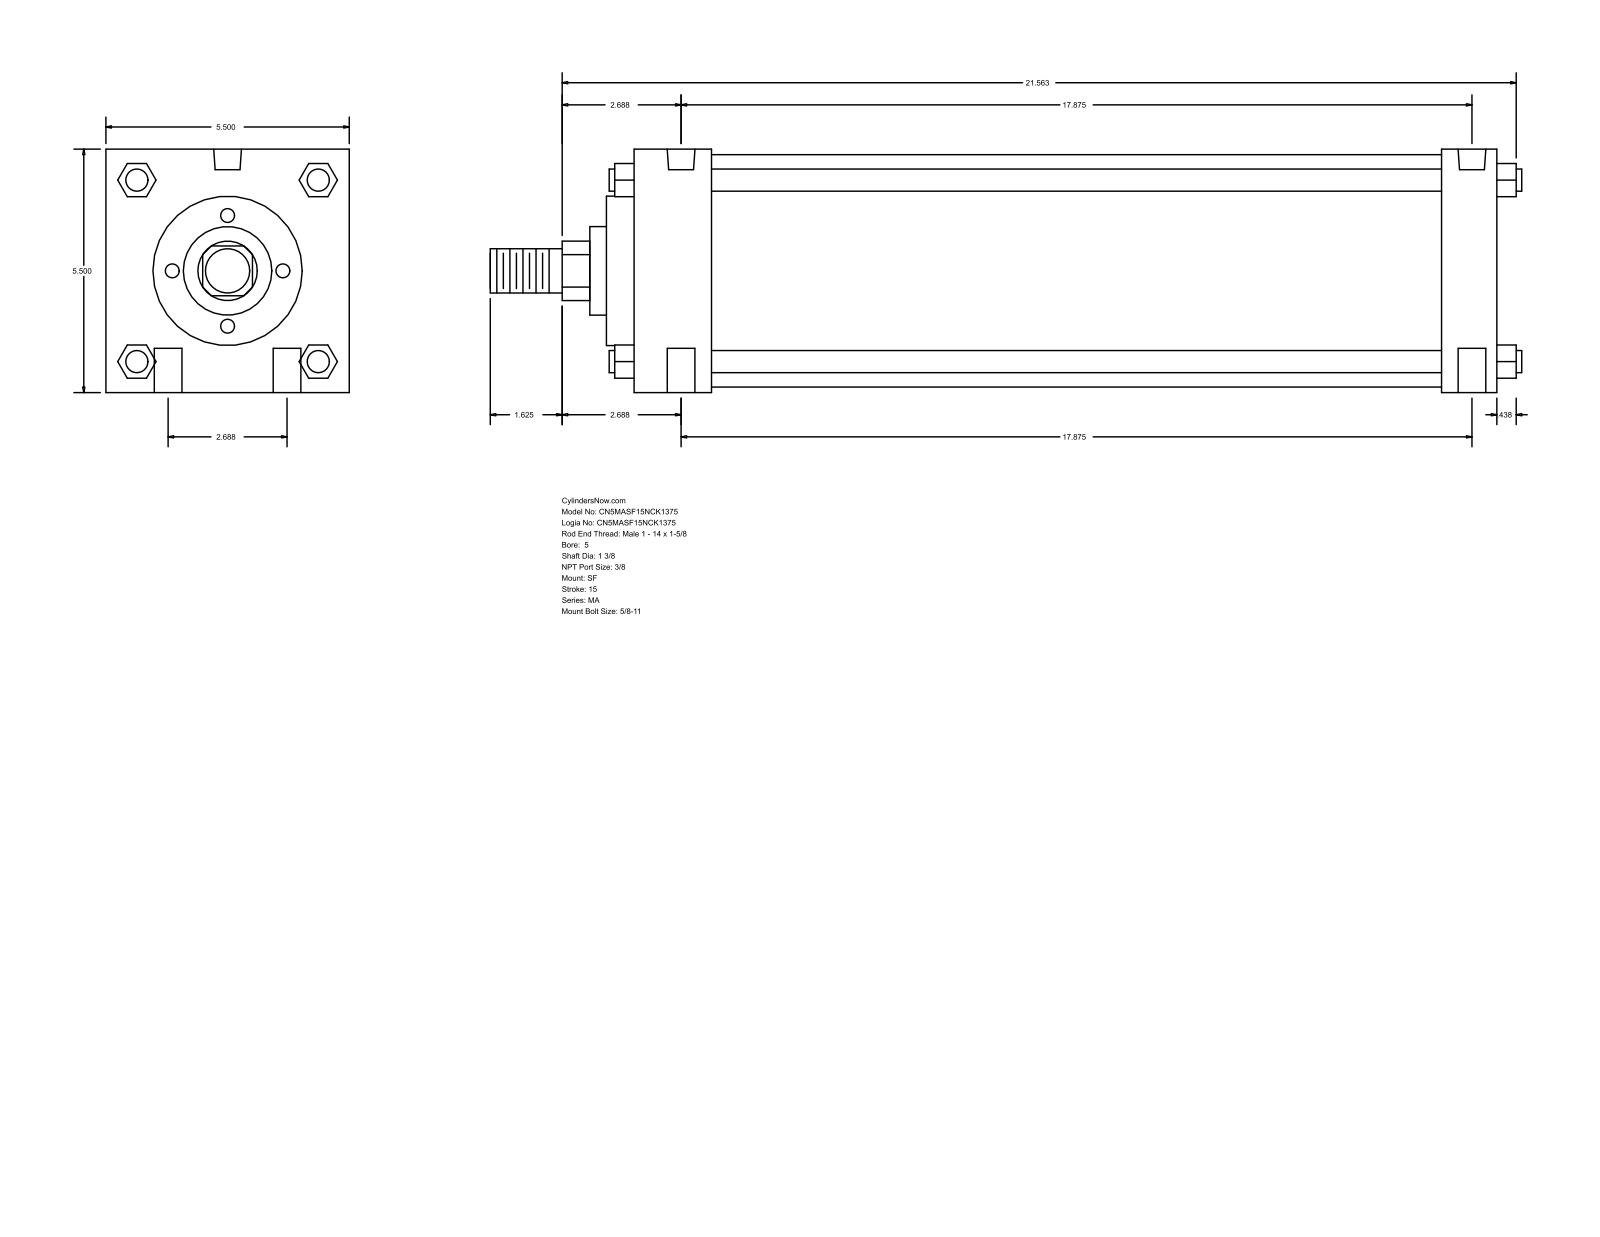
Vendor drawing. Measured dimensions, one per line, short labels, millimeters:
name: MA_SF__0500_1.375
written by: GSSL Pune (CONFIG_CONTROL_DESIGN)
unit: mm
bodies: 0 solids, 126 faces (95 planar, 31 cylindrical, 0 other)
size: 592.14 × 139.7 × 139.7
holes: 4× ⌀15.88, 2× ⌀11.11, 2× ⌀15.93
bosses: 4× ⌀12.7, 1× ⌀133.35, 1× ⌀85.72, 1× ⌀50.8, 1× ⌀34.92, 1× ⌀25.4
rounds: 1× R17.06
face distances: 139.7, 495.31, 44.45, 463.55, 419.1, 450.86, 31.76, 15.87, 60.32, 479.42
hole spacings: 34.13, 455.31, 454.03, 68.26, 459.13, 444.49
